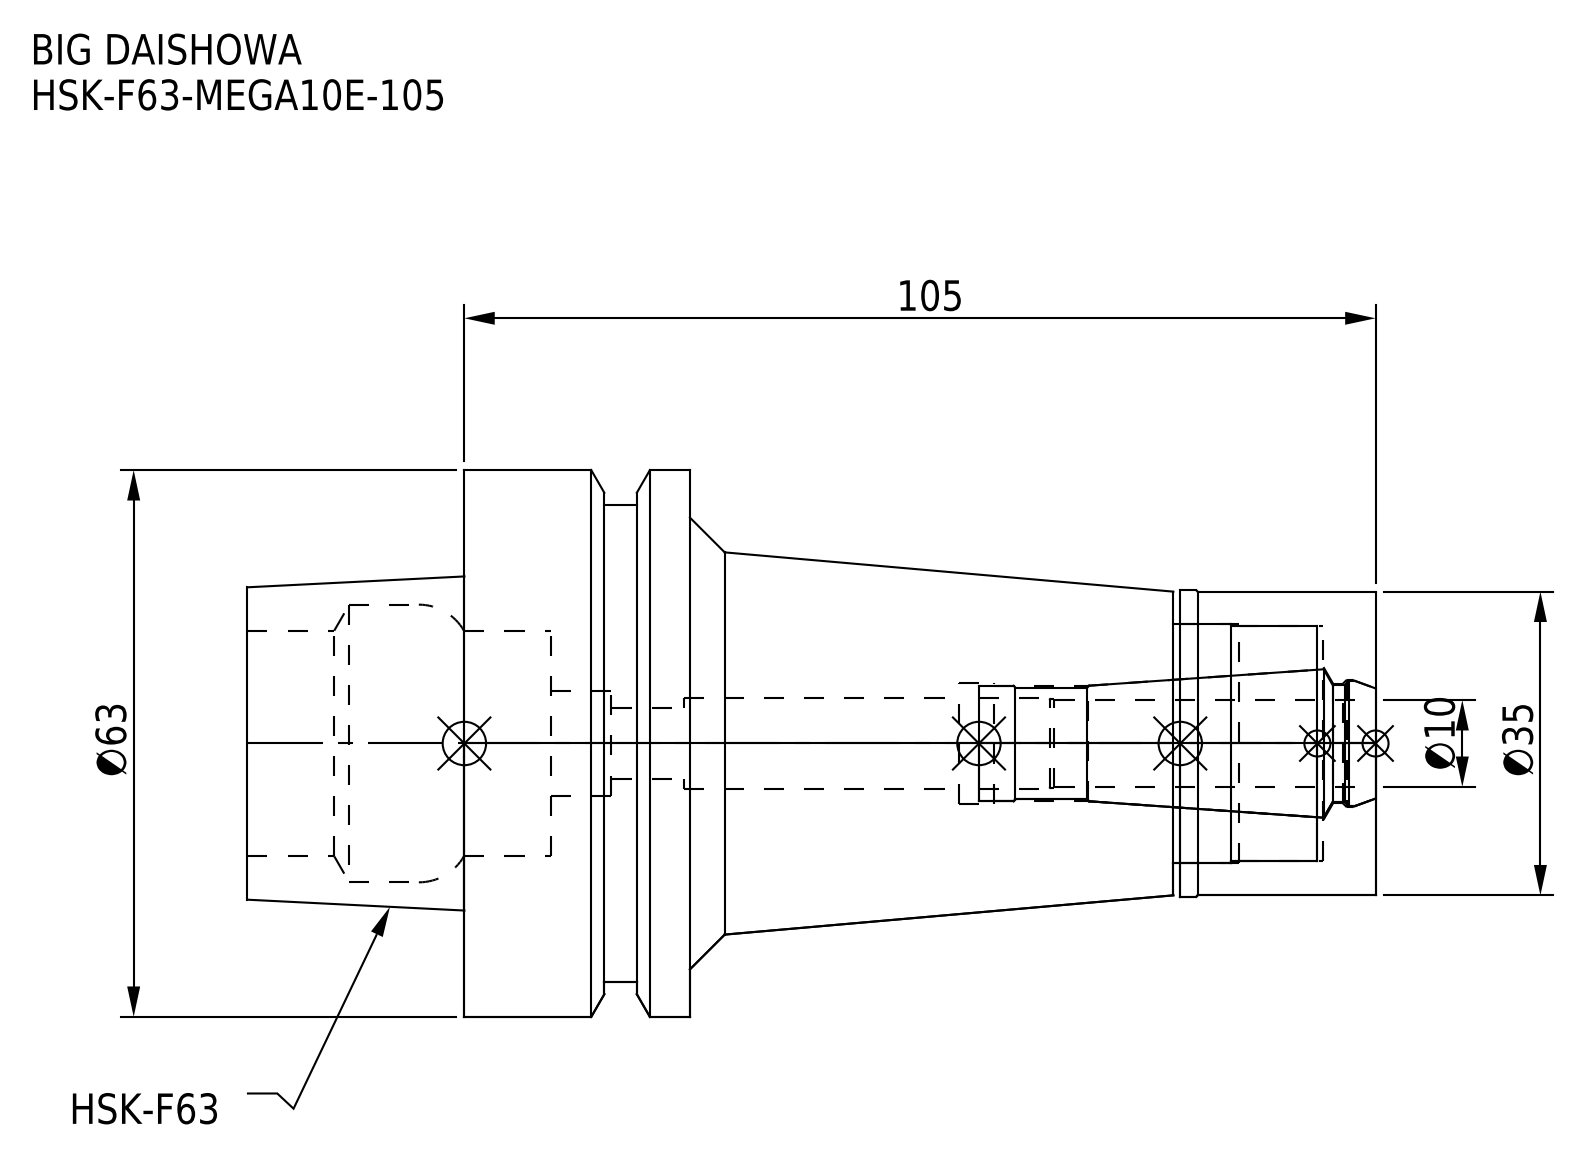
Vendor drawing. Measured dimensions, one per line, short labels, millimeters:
name: HSK-F63-MEGA10E-105_1.stp; HF63ME10105-100_ASM.stp; HSK-F63-MEGA10E-105-100.stp; MEN10_1.stp (+3 more)
written by: SolidWorks 2019 (CONFIG_CONTROL_DESIGN)
unit: mm
bodies: 2 solids, 81 faces (17 planar, 40 cylindrical, 24 other)
size: 130 × 63 × 63
volume: 163 718 mm³; area: 35 046 mm²
holes: 1× ⌀8.25, 1× ⌀10.4, 1× ⌀12, 1× ⌀13.3, 1× ⌀13.8, 1× ⌀13.9, 1× ⌀14.7, 1× ⌀26, 1× ⌀27, 1× ⌀27.5, 1× ⌀32
bosses: 1× ⌀63, 1× ⌀55, 1× ⌀35.3, 1× ⌀35
face distances: 26, 79, 105, 130, 51, 25, 95.05, 16.05, 9.95, 34.95
